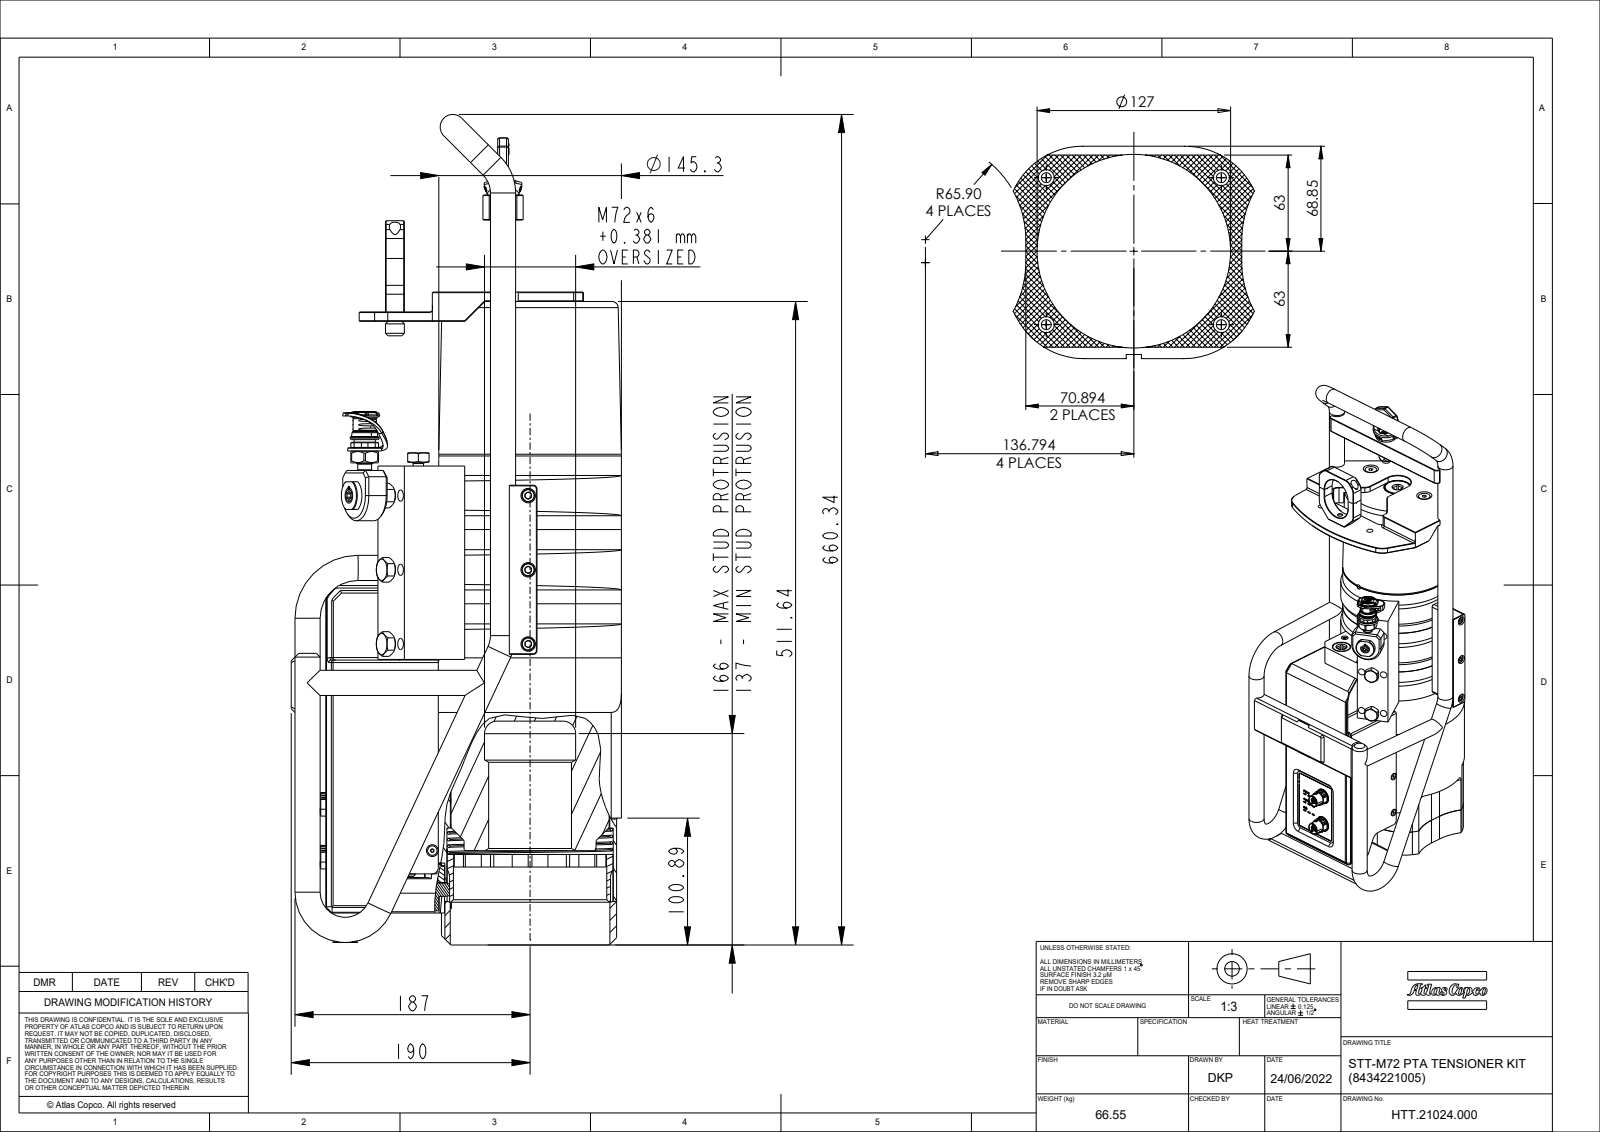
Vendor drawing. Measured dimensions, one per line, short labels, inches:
name: 8500 GEAR HOUSING - UPPER; M5 x 16 LG SOCKET HEAD CAP SCREW_BS EN ISO 4762 M5 x 16 - 16N; STT OVERLAY; M6 x 45 LG SOCKET HEAD CAP SCREW_BS EN ISO 4762 M6 x 45 - 45N (+8 more)
written by: SolidWorks 2020 (AUTOMOTIVE_DESIGN)
unit: in
bodies: 215 solids, 17427 faces (10244 planar, 3860 cylindrical, 3323 other)
size: 25.998 × 10.341 × 8.78
volume: 617 in³; area: 3 405 in²
holes: 28× ⌀0.197, 21× ⌀0.165, 21× ⌀0.217, 16× ⌀0.008, 16× ⌀0.045, 15× ⌀0.236, 15× ⌀0.354, 13× ⌀0.098, 11× ⌀0.118, 10× ⌀0.079, 10× ⌀0.096, 10× ⌀0.17
bosses: 49× ⌀0.02, 21× ⌀0.197, 19× ⌀0.236, 16× ⌀0.335, 16× ⌀0.031, 16× ⌀0.024, 14× ⌀0.394, 13× ⌀0.118
rounds: 102× R0.008, 102× R0.01, 100× R0.079, 65× R0.039, 60× R0.991, 50× R0.385, 48× R0.004, 38× R0.118
face distances: 0.157, 2.323, 4.646, 0.866, 0.295, 0.591, 0.622, 0.787, 1.457, 3.484
hole spacings: 2.323, 2.397, 0.591, 2.606, 4.646, 4.683, 0.296, 1.181
